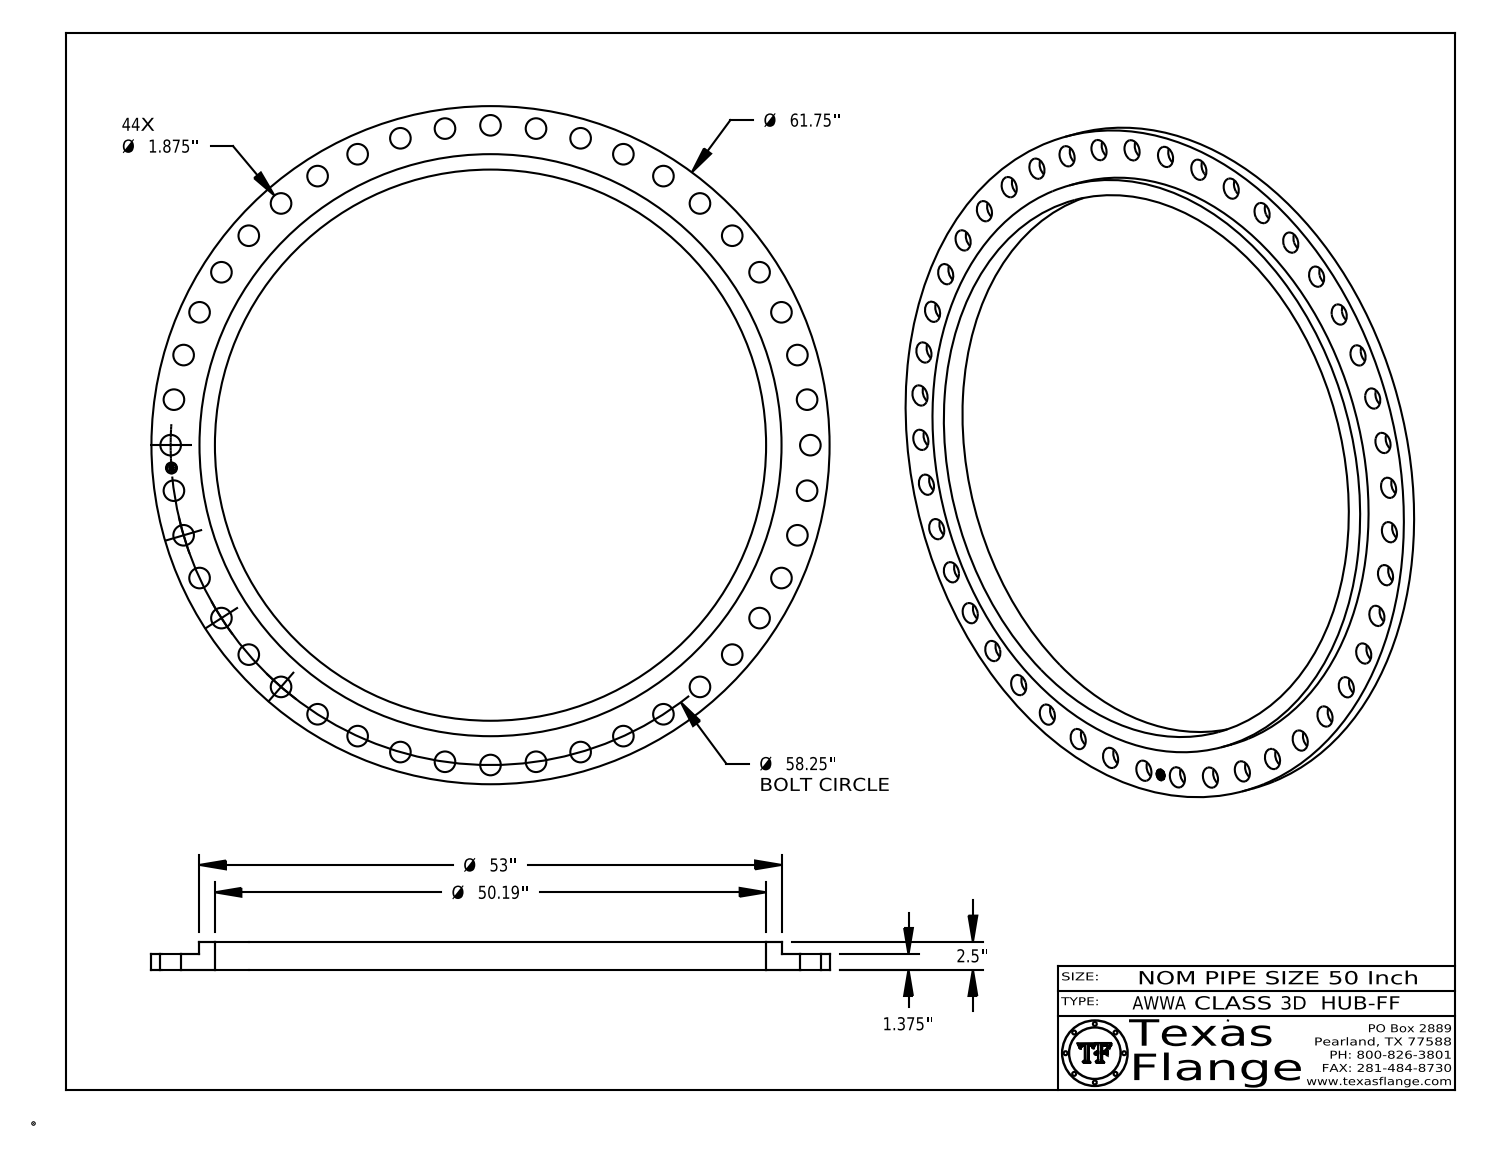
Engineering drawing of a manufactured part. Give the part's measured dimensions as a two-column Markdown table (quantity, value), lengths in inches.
| quantity | value |
| --- | --- |
| part name | AWWA Class 3D-HUB-FF |
| STEP written by | CATIA V5 STEP AP214 (AUTOMOTIVE_DESIGN) |
| units | inches |
| bodies | 1 solid, 482 faces (368 planar, 114 cylindrical, 0 other) |
| overall size | 61.75 × 61.75 × 2.5 |
| volume | 1 487 in³ |
| surface area | 2 994 in² |
| round holes (diameter × count) | 1.875 × 44, 1 × 1, 50.19 × 1 |
| round bosses / shafts (diameter × count) | 0.061 × 8, 61.75 × 1, 53 × 1, 0.788 × 1 |
| main face-to-face distances | 1.375, 2.5, 1.125, 0.015, 1.36, 1.14, 0.298, 0.292, 0.054, 0.193 |
| hole center spacings | 12.382, 20.356, 8.29, 4.156, 29.125, 16.411, 24.198, 51.125 |
